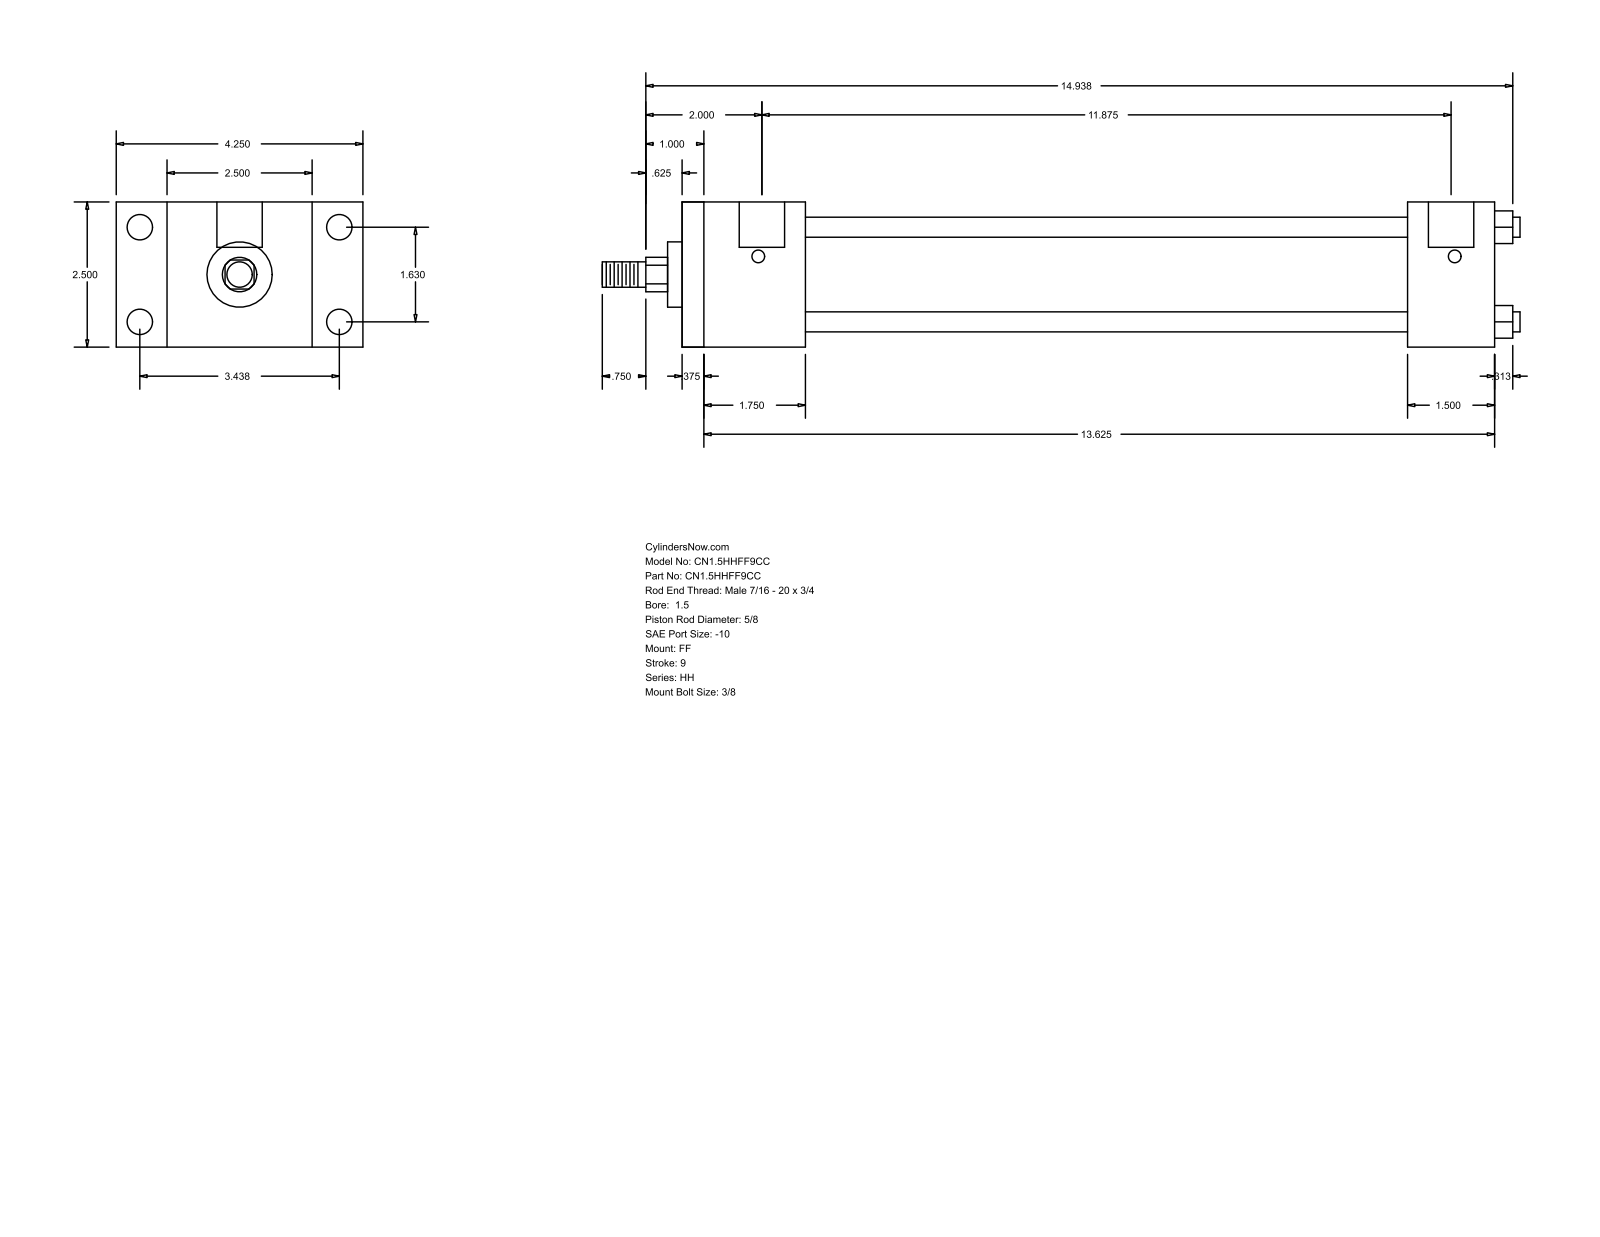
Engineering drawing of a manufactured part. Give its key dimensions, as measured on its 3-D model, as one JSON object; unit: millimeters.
{"part_name": "HH_FF__0150_0.625", "step_written_by": "GSSL Pune (CONFIG_CONTROL_DESIGN)", "units": "millimeters", "bodies": {"solids": 0, "faces": 92, "planar": 64, "cylindrical": 28, "other": 0}, "overall_size": [401.64, 107.95, 63.5], "round_holes": [[5.56, 4], [11.13, 4], [19.84, 2]], "round_bosses_or_shafts": [[8.76, 4], [44.45, 1], [28.57, 1], [15.88, 1], [11.11, 1]], "partial_cylinders_radius": [[7.54, 1]], "face_to_face_distances": [63.5, 355.6, 38.1, 9.52, 346.08, 44.45, 53.97, 301.63, 317.5, 307.98], "hole_center_spacings": [41.4, 87.32, 96.64, 304.8, 1.58, 1.59, 301.63, 303.21]}
